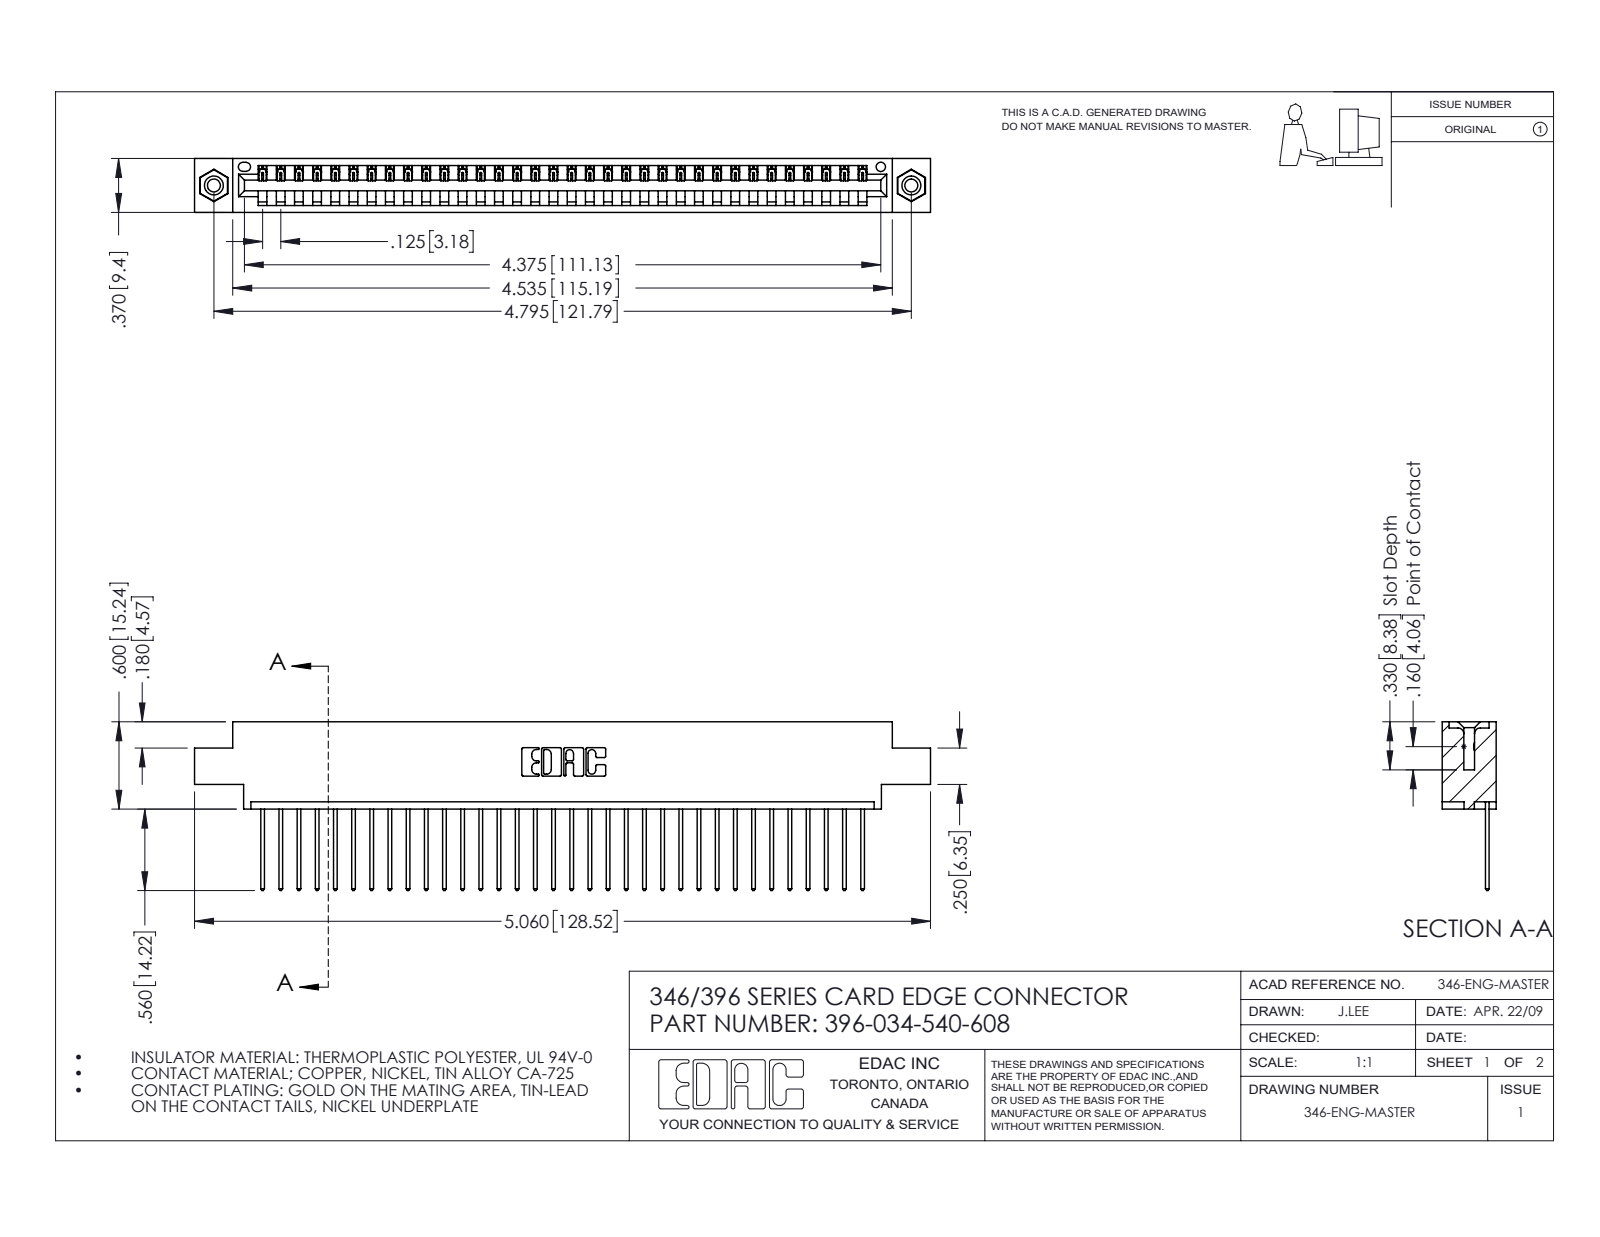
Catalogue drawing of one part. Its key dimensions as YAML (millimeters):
part_name: "346 Part_0.170 Offset - 0.156 Dia-TI; 396-034-540-608; 345-250-001_345-250-003-102; 345-292-001_345-293-140"
step_written_by: "SolidWorks 2016 (CONFIG_CONTROL_DESIGN)"
units: millimeters
bodies: {solids: 37, faces: 2158, planar: 1472, cylindrical: 670, other: 16}
overall_size: [128.5, 29.5, 9.4]
volume: 12100
surface_area: 15590
round_holes:
  - {diameter: 2.3, count: 2}
  - {diameter: 3.2, count: 2}
  - {diameter: 4, count: 2}
  - {diameter: 1.6, count: 1}
round_bosses_or_shafts:
  - {diameter: 3.9, count: 2}
partial_cylinders:
  - {radius: 0.2, count: 68}
  - {radius: 0.3, count: 68}
  - {radius: 0.3, count: 22}
  - {radius: 0.2, count: 6}
  - {radius: 0.8, count: 6}
  - {radius: 0.7, count: 3}
  - {radius: 0.8, count: 2}
  - {radius: 1, count: 2}
face_to_face_distances: [1.2, 8.2, 9.4, 6.4, 1.8, 7.6, 0.6, 5.6, 3.8, 2.5]
hole_center_spacings: [6.2, 116.5, 121.8]
